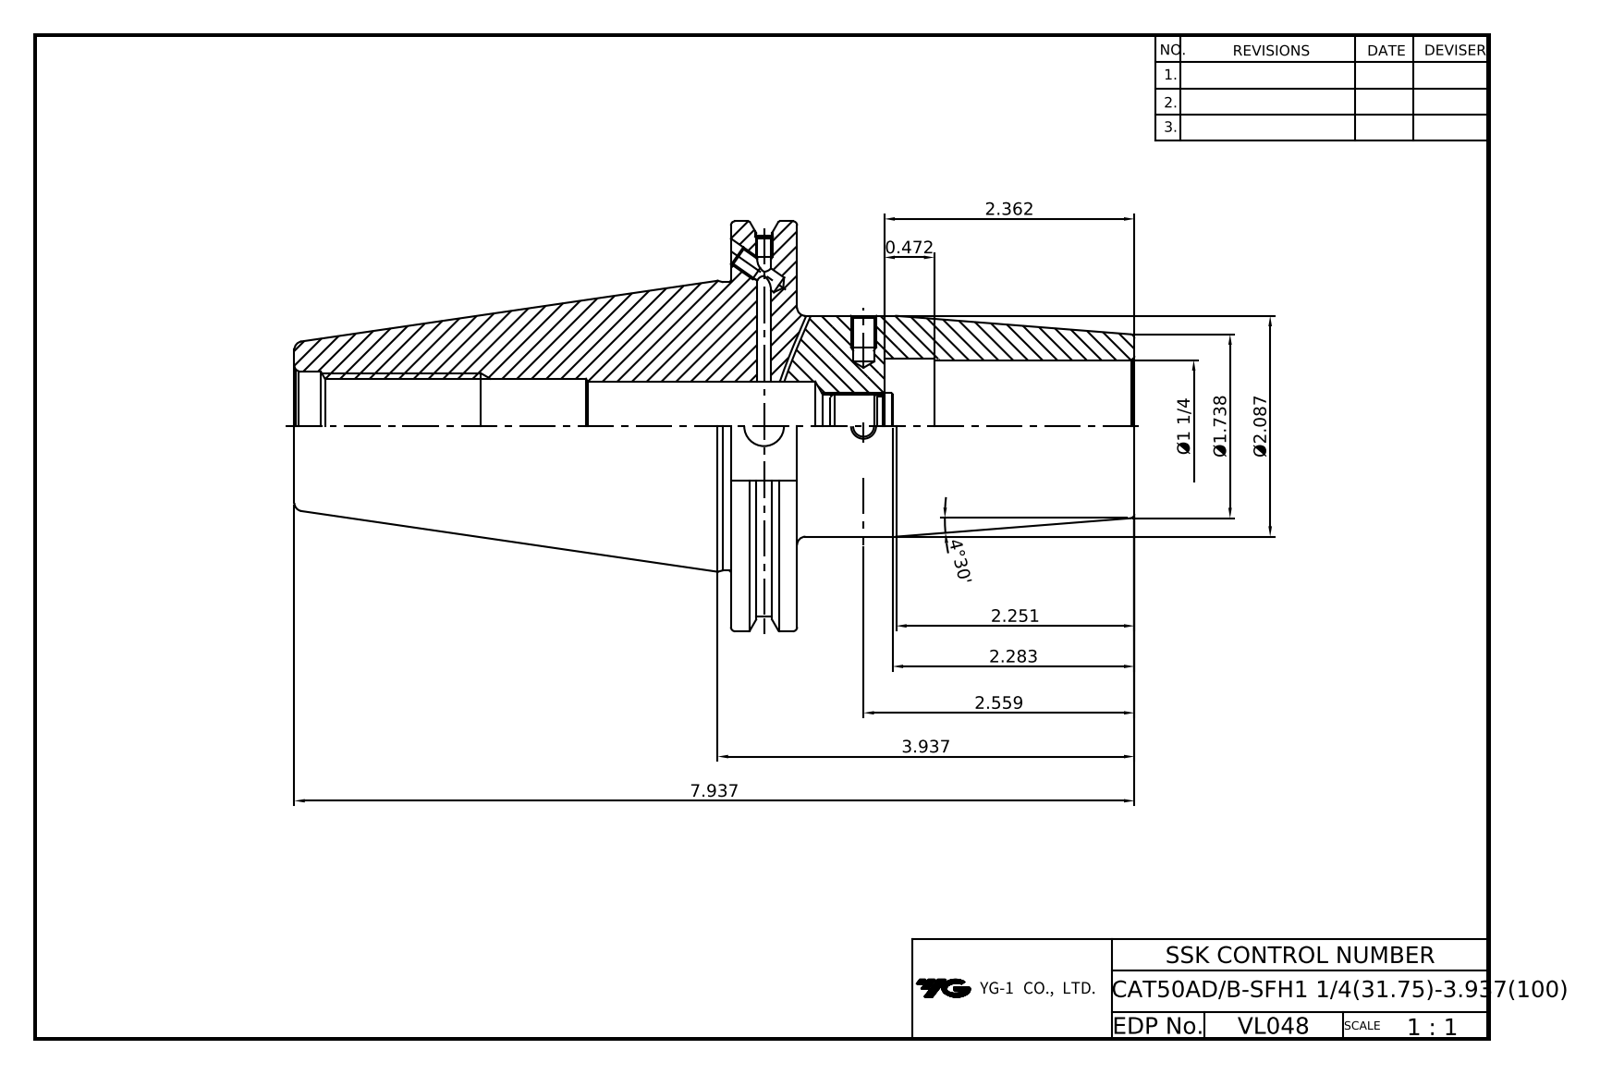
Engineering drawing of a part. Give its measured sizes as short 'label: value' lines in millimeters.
name: LO-CAT50ADB-SFH31.75-100
written by: Autodesk Inventor 2025 (AUTOMOTIVE_DESIGN)
unit: mm
bodies: 1 solid, 84 faces (37 planar, 26 cylindrical, 21 other)
size: 201.6 × 98.42 × 94.69
volume: 425 378 mm³; area: 63 759 mm²
holes: 2× ⌀3.24, 2× ⌀4.13, 2× ⌀4.2, 2× ⌀5, 1× ⌀9.53, 1× ⌀14.92, 1× ⌀21.97, 1× ⌀26.2, 1× ⌀31.75, 1× ⌀32.95
bosses: 1× ⌀98.42, 1× ⌀91.29, 1× ⌀69.25, 1× ⌀53
face distances: 15.88, 36.83, 20.95, 104.77, 120.65, 141.6, 201.6, 96.83, 80.95, 60
